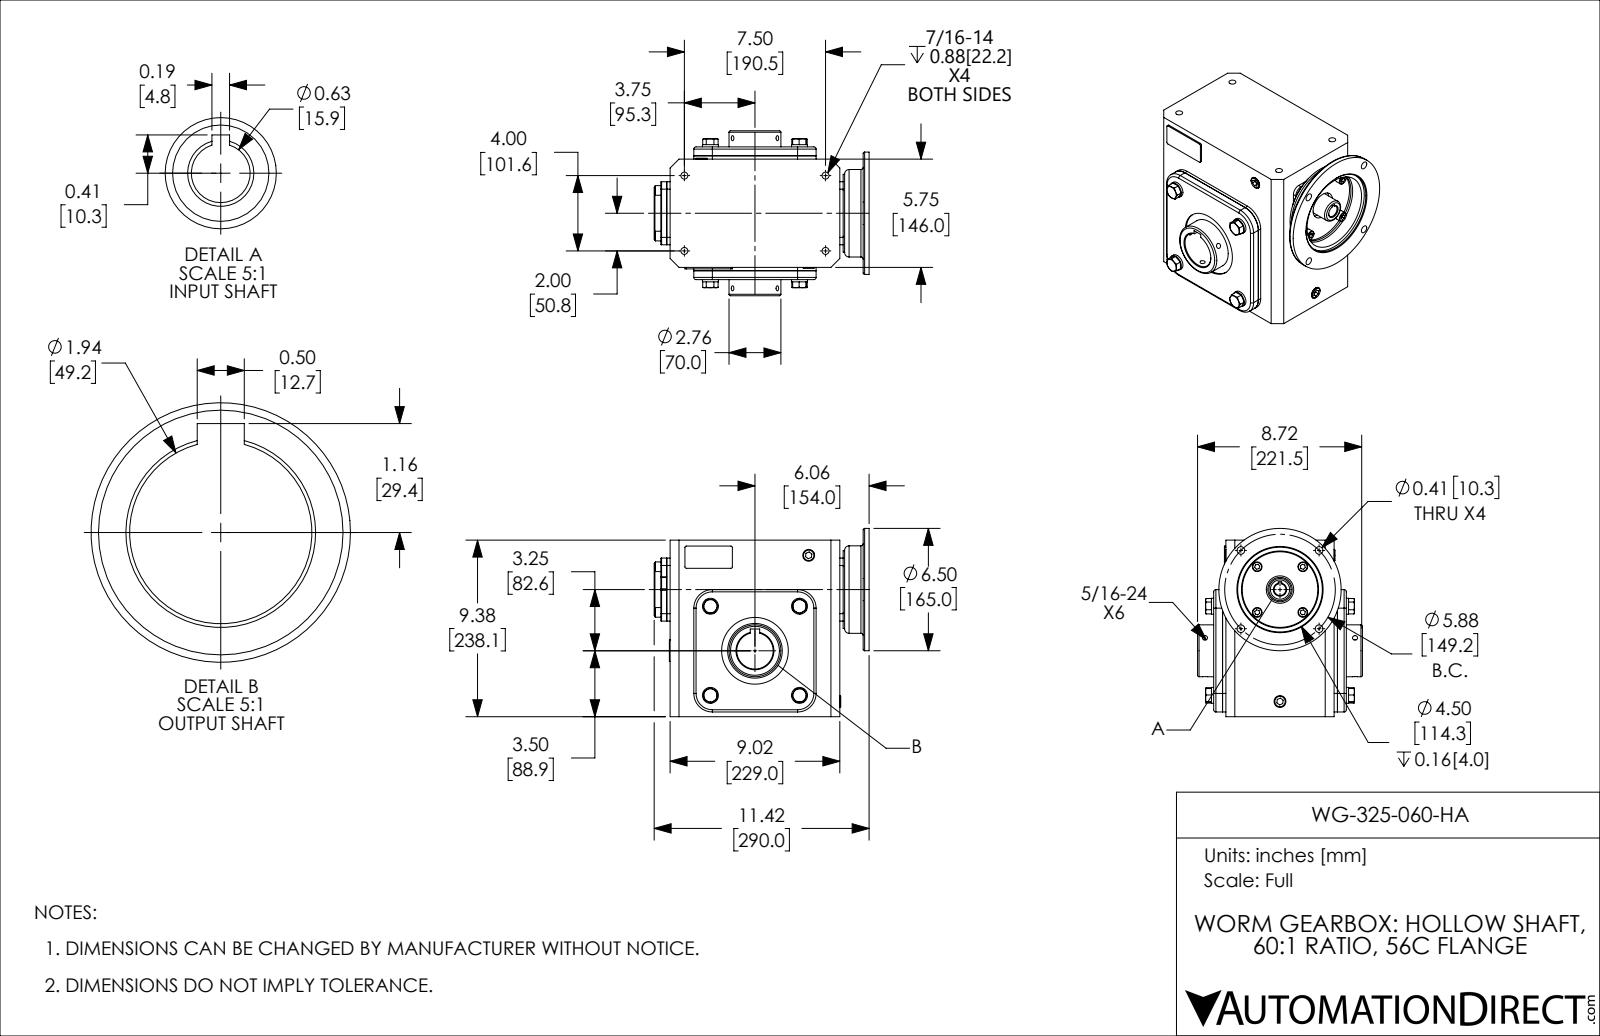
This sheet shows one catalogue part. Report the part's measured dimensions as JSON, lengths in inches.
{"part_name": "WG-325-060-HA", "step_written_by": "SolidWorks 2017 (AUTOMOTIVE_DESIGN)", "units": "inches", "bodies": {"solids": 39, "faces": 587, "planar": 314, "cylindrical": 178, "other": 95}, "overall_size": [11.417, 9.998, 8.76], "volume_in3": 515.8, "surface_area_in2": 982.1, "round_holes": [[0.272, 6], [0.368, 4], [0.406, 4], [0.628, 3], [0.591, 1], [0.625, 1], [0.978, 1], [1.181, 1], [1.457, 1], [1.937, 1], [2.441, 1], [2.756, 1]], "round_bosses_or_shafts": [[0.846, 4], [0.512, 4], [6.496, 1], [4.646, 1], [4.134, 1], [2.835, 1], [1.142, 1]], "partial_cylinders_radius": [[0.118, 8], [0.079, 7], [0.394, 4], [0.906, 4], [0.984, 4], [0.02, 2], [0.039, 2]], "face_to_face_distances": [0.079, 0.177, 6.496, 0.394, 0.571, 6.319, 5.925, 6.398, 6.969, 0.472], "hole_center_spacings": [2.937, 4.154, 4.244, 7.064, 7.972, 2.385, 4, 4.389]}
